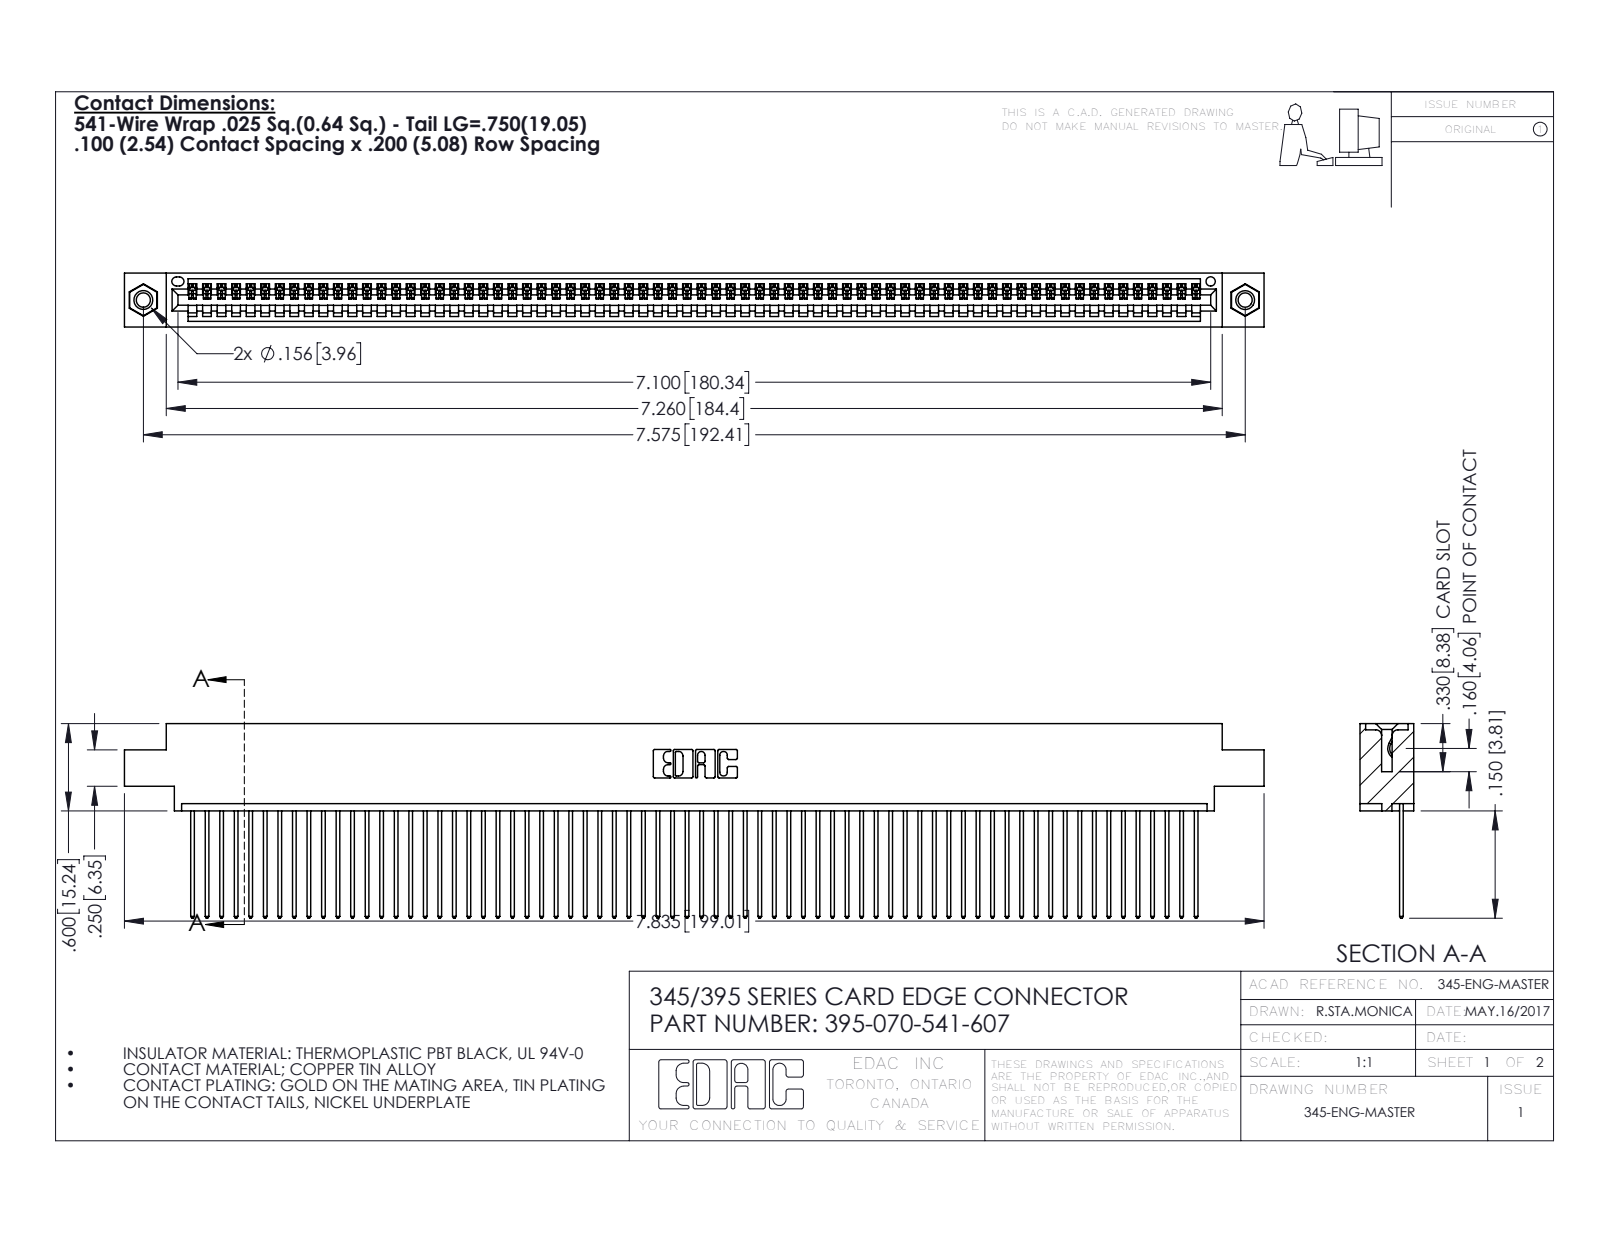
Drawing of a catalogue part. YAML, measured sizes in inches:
part_name: "395-070-541-607; 345-250-001_345-250-005-103; 345-292-001_345-293-141; 345 Part_0.170 Offset - 0.156 Dia-TI"
step_written_by: "SolidWorks 2016 (CONFIG_CONTROL_DESIGN)"
units: inches
bodies: {solids: 73, faces: 4250, planar: 2916, cylindrical: 1318, other: 16}
overall_size: [7.835, 1.337, 0.37]
volume: 1.174
surface_area: 42.56
round_holes:
  - {diameter: 0.098, count: 2}
  - {diameter: 0.125, count: 2}
  - {diameter: 0.156, count: 2}
  - {diameter: 0.064, count: 1}
round_bosses_or_shafts:
  - {diameter: 0.155, count: 2}
partial_cylinders:
  - {radius: 0.006, count: 140}
  - {radius: 0.01, count: 140}
  - {radius: 0.01, count: 22}
  - {radius: 0.007, count: 6}
  - {radius: 0.031, count: 6}
  - {radius: 0.026, count: 3}
  - {radius: 0.031, count: 2}
  - {radius: 0.04, count: 2}
face_to_face_distances: [0.072, 0.298, 0.098, 0.272, 0.025, 0.37, 0.2, 0.225, 0.175, 0.149]
hole_center_spacings: [0.27, 7.339, 7.575]
